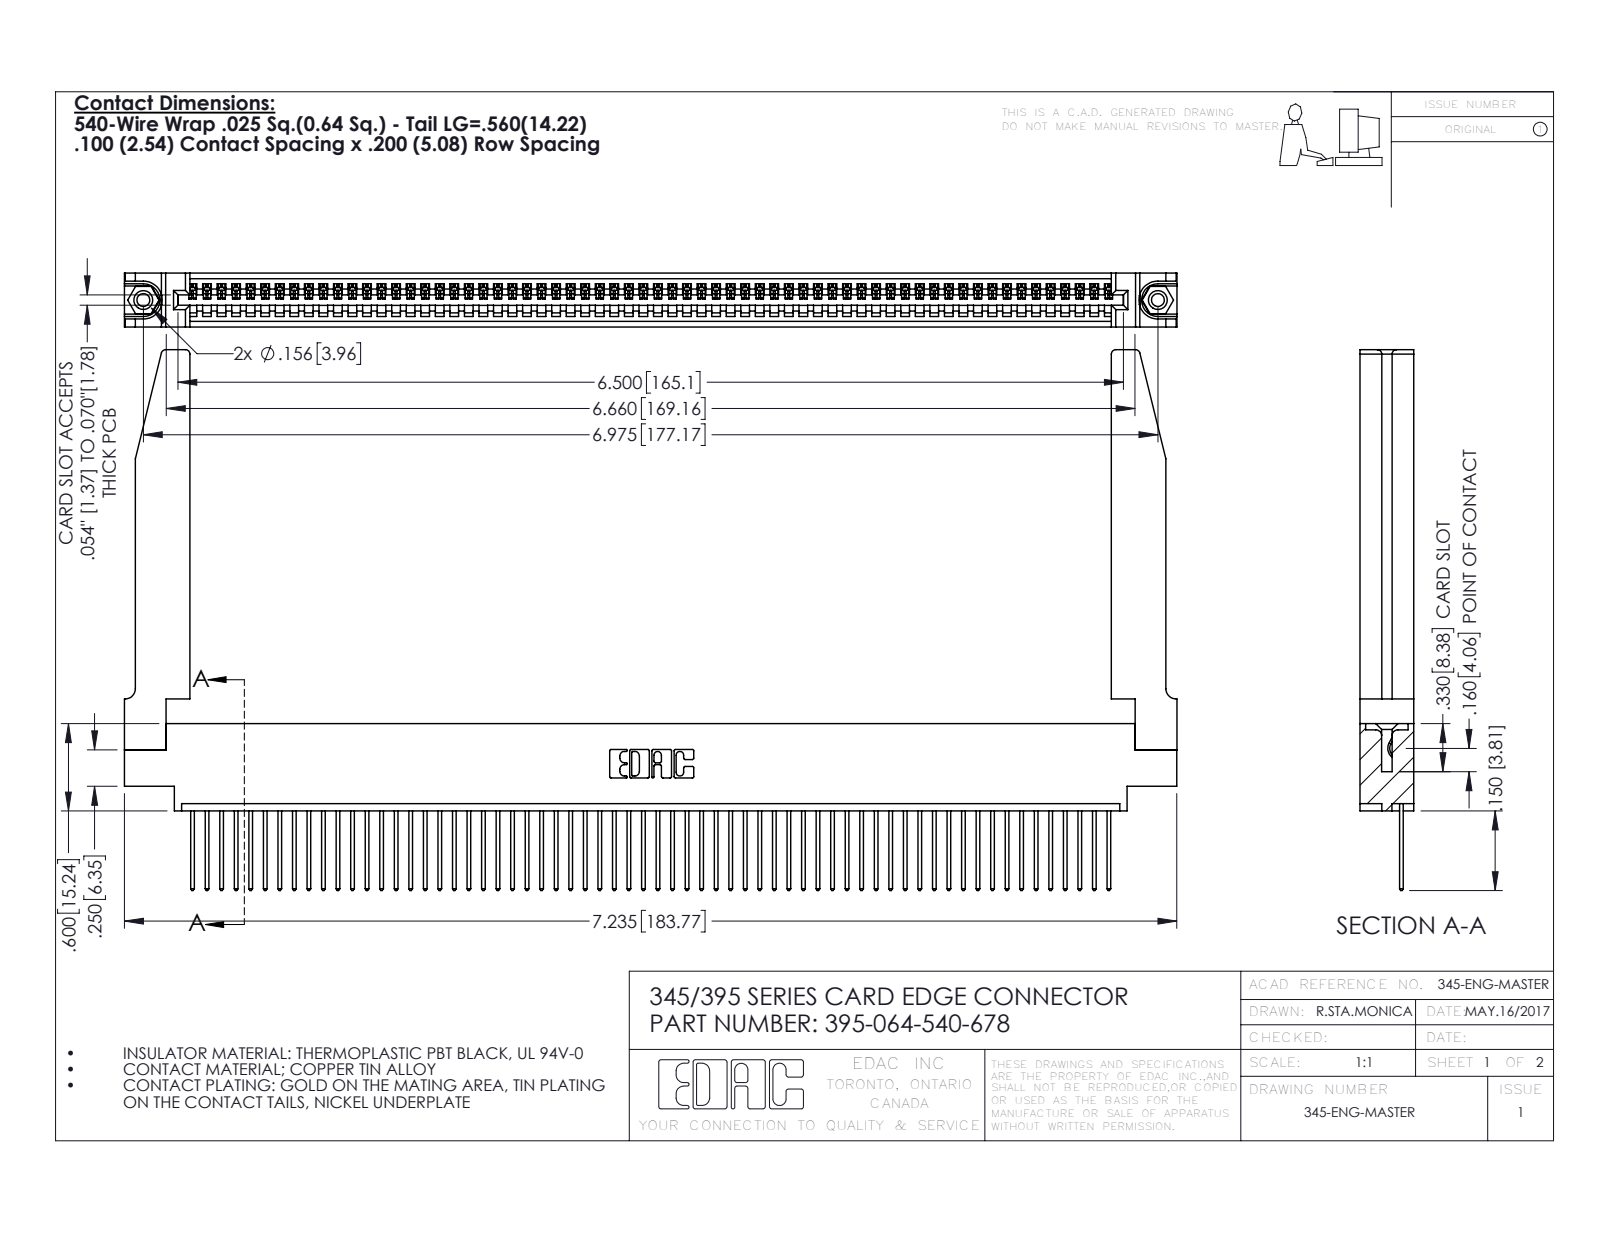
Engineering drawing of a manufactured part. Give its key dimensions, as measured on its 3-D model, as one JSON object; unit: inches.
{"part_name": "345-250-001_345-250-001-102; 395-064-540-678; 345-220-078_345-220-078; 345-292-001_345-293-140 (+1 more)", "step_written_by": "SolidWorks 2016 (CONFIG_CONTROL_DESIGN)", "units": "inches", "bodies": {"solids": 69, "faces": 4076, "planar": 2786, "cylindrical": 1238, "other": 52}, "overall_size": [7.236, 3.717, 0.37], "volume_in3": 1.549, "surface_area_in2": 48.51, "round_holes": [[0.089, 2], [0.125, 2], [0.156, 2], [0.064, 1]], "round_bosses_or_shafts": [[0.155, 2]], "partial_cylinders_radius": [[0.006, 128], [0.01, 128], [0.01, 22], [0.03, 8], [0.007, 6], [0.031, 6], [0.026, 3], [0.031, 2]], "face_to_face_distances": [0.072, 0.37, 0.298, 0.098, 0.272, 0.025, 0.2, 0.225, 0.148, 0.15], "hole_center_spacings": [0.27, 6.739, 6.975]}
